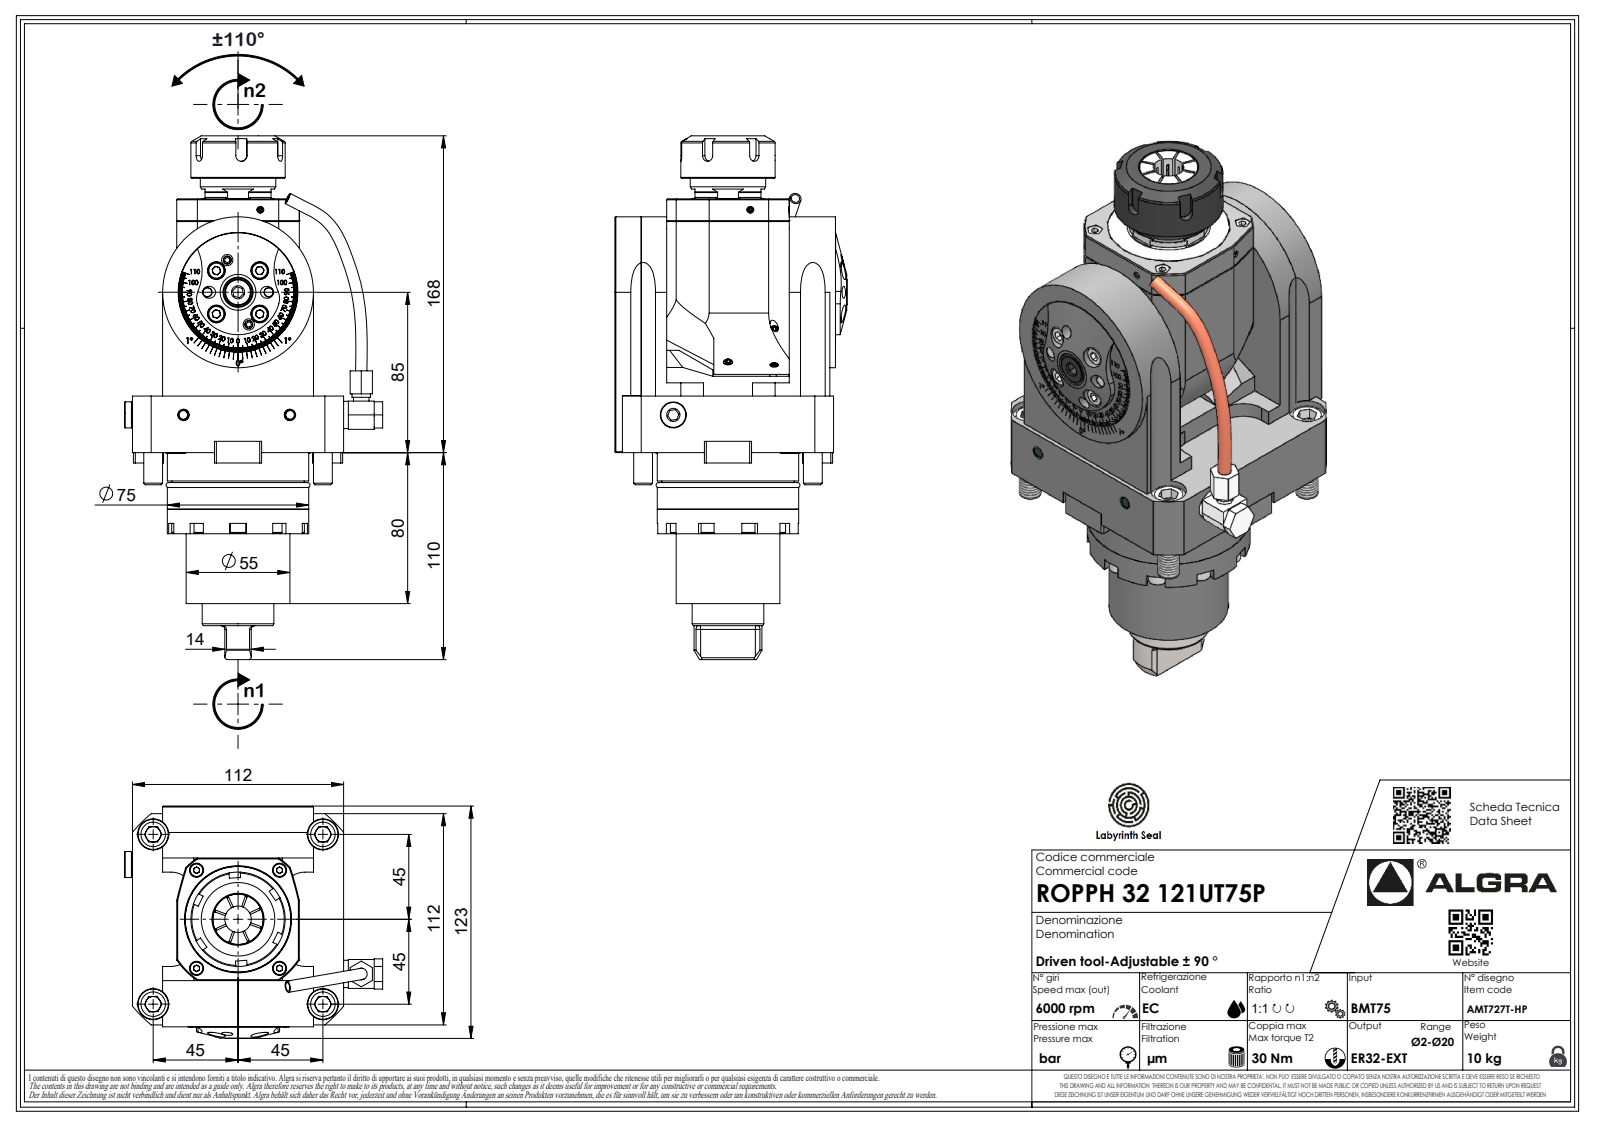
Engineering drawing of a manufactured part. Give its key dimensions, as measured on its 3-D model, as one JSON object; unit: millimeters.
{"part_name": "ROPPH32121UT75P", "step_written_by": "SolidWorks 2023 (AUTOMOTIVE_DESIGN)", "units": "millimeters", "bodies": {"solids": 1, "faces": 651, "planar": 436, "cylindrical": 105, "other": 110}, "overall_size": [277.61, 132.7, 123], "volume_mm3": 1476000, "surface_area_mm2": 125233, "round_holes": [[2.1, 1], [5, 1]], "round_bosses_or_shafts": [[80, 1], [75, 1], [70.2, 1], [55, 1], [50, 1], [40, 1], [38, 1], [14.5, 1]], "partial_cylinders_radius": [[4.35, 10], [0.33, 7], [0.52, 7], [3.7, 7], [2, 6], [4, 6], [3, 5], [12, 4]], "face_to_face_distances": [23.5, 88.5, 16, 65, 30, 96, 80, 7.5, 72.5, 24.5]}
